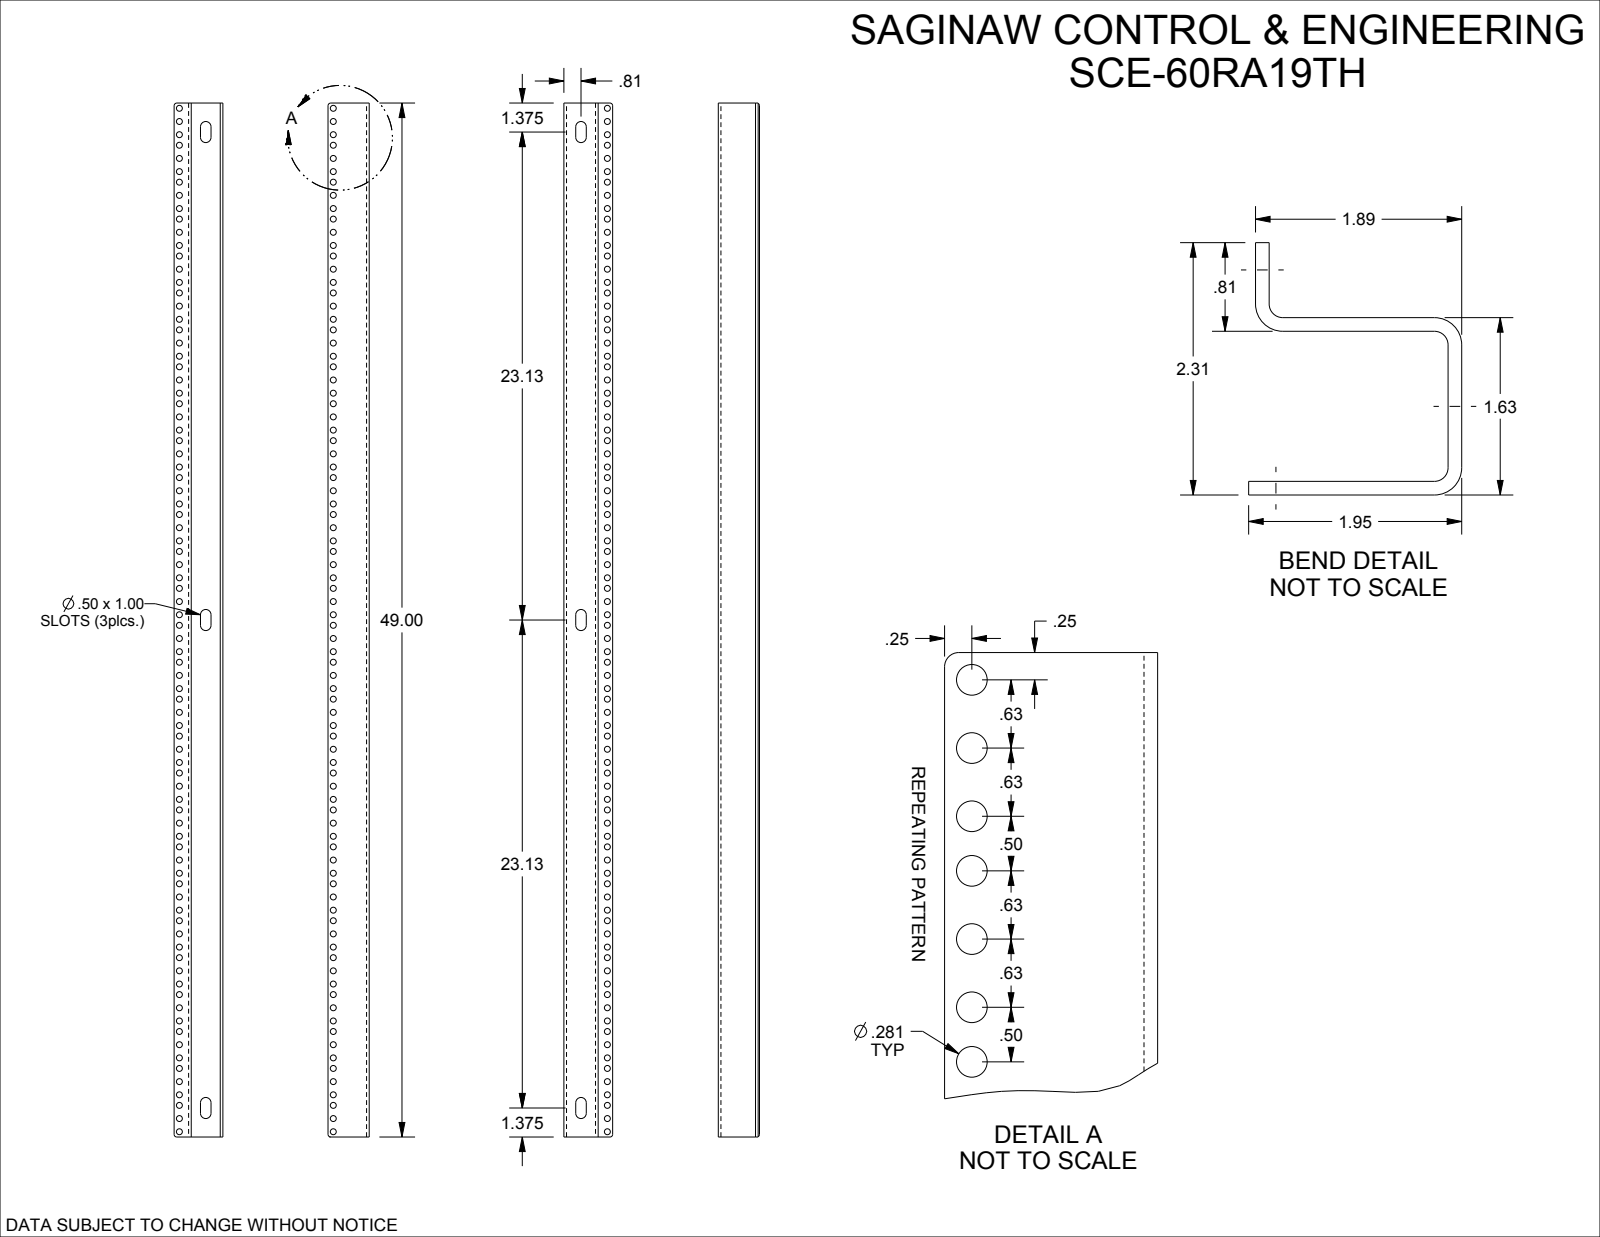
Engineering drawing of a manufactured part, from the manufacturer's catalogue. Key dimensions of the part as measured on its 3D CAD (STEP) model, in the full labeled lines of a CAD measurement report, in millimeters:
Part name (STEP PRODUCT): SCE-60RA19TH
STEP written by: SolidWorks 2019 (CONFIG_CONTROL_DESIGN)
Units: millimetres
Bodies: 2 solids, 404 faces (36 planar, 368 cylindrical, 0 other)
Overall size (bounding box): 1244.6 × 551.7 × 58.7
Volume: 1 089 000 mm³ · Surface area: 728 400 mm²
Round holes (diameter × count): ⌀7.1 ×257
Partial cylindrical surfaces — rounded edges, fillets, slot ends (radius × count): R6.4 ×13, R3.2 ×8, R3.3 ×6
Main face-to-face distances: 3.2, 38.1, 41.3, 34.9, 3.2, 503.6, 44.8, 548.5, 551.7, 545.3
Hole centre spacings: 44.5, 88.9, 133.4, 177.8, 222.3, 15.9, 15.9, 31.8
